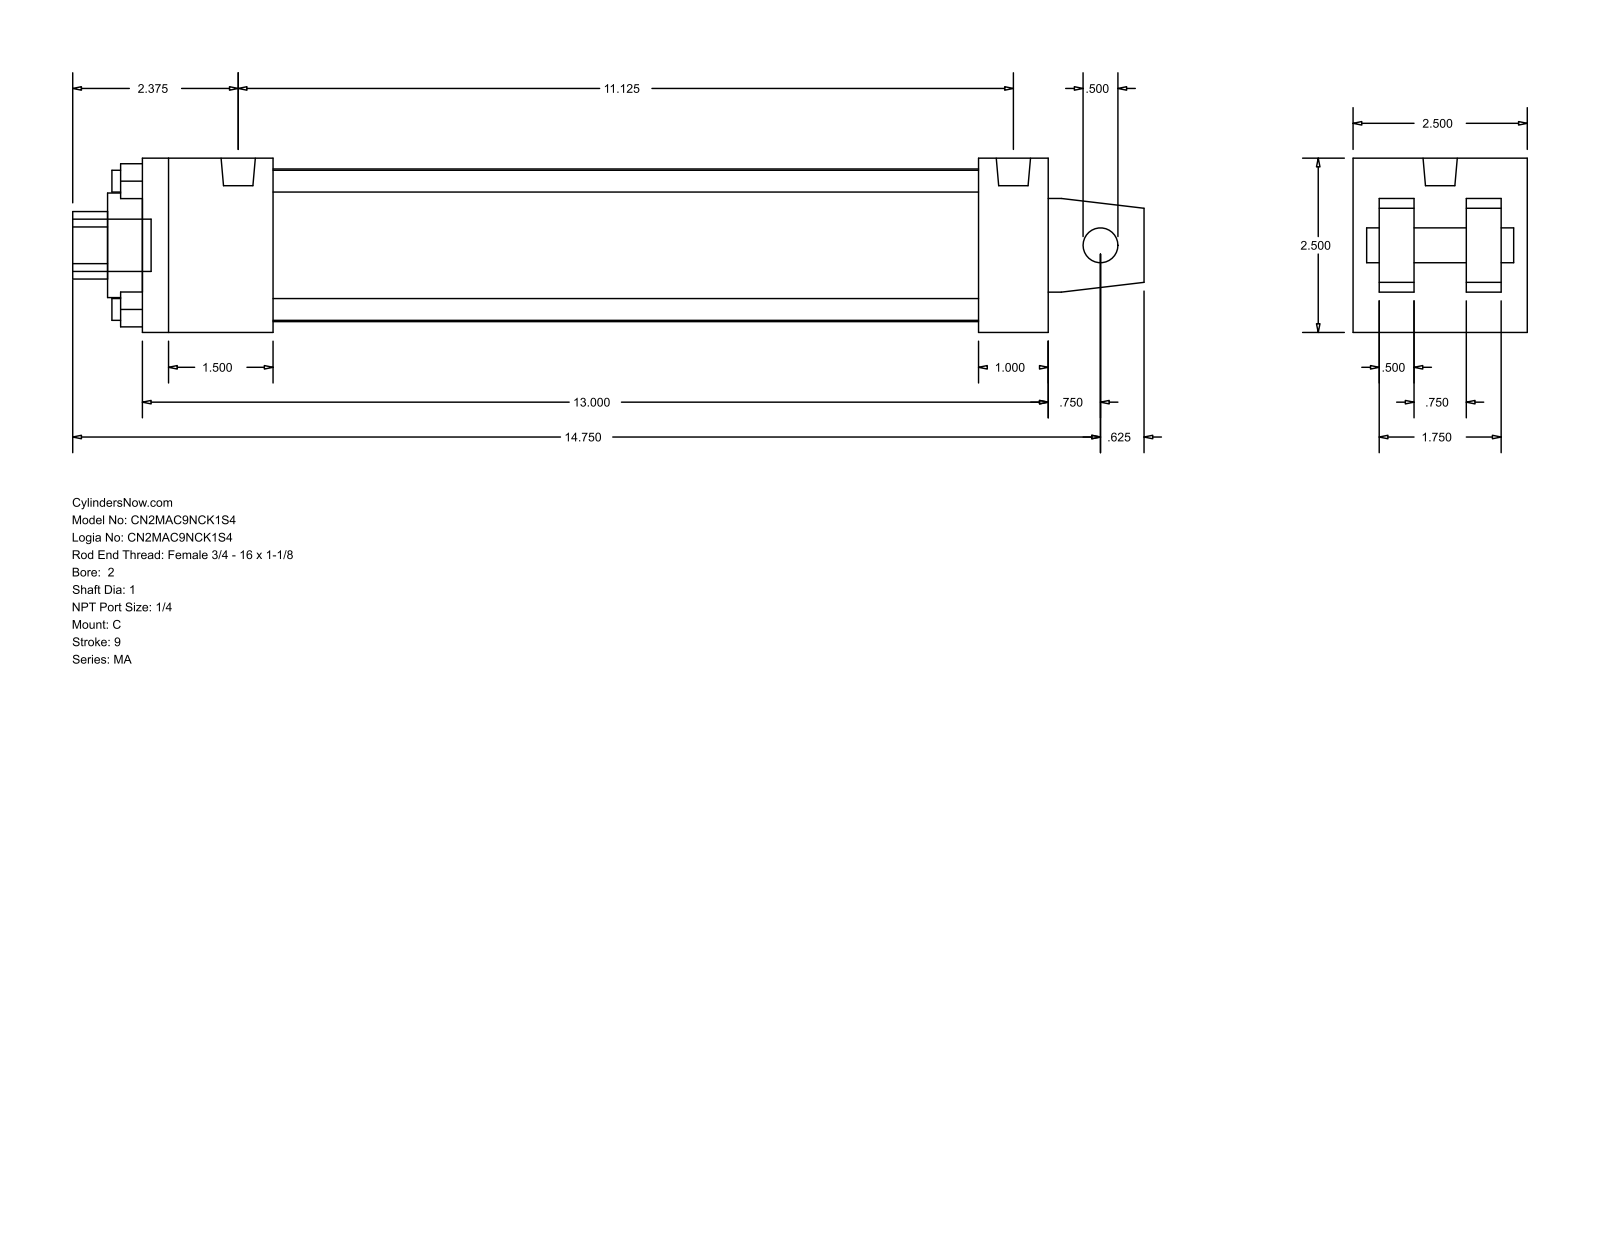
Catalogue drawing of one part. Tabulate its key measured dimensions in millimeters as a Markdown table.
| quantity | value |
| --- | --- |
| part name | MA_C__0200_1 |
| STEP written by | GSSL Pune (CONFIG_CONTROL_DESIGN) |
| units | millimeters |
| bodies | 0 solids, 103 faces (76 planar, 27 cylindrical, 0 other) |
| overall size | 390.52 × 63.5 × 63.5 |
| round holes (diameter × count) | 7.94 × 4, 12.7 × 1, 25.4 × 1, 38.1 × 1, 55.63 × 1 |
| round bosses / shafts (diameter × count) | 7.94 × 4, 12.49 × 2, 19.05 × 1 |
| partial cylindrical surfaces (radius × count) | 12.29 × 1 |
| main face-to-face distances | 63.5, 12.7, 330.2, 22.22, 41.28, 9.52, 53.98, 31.76, 47.63, 25.4 |
| hole center spacings | 33.05, 46.74, 66.1 |
